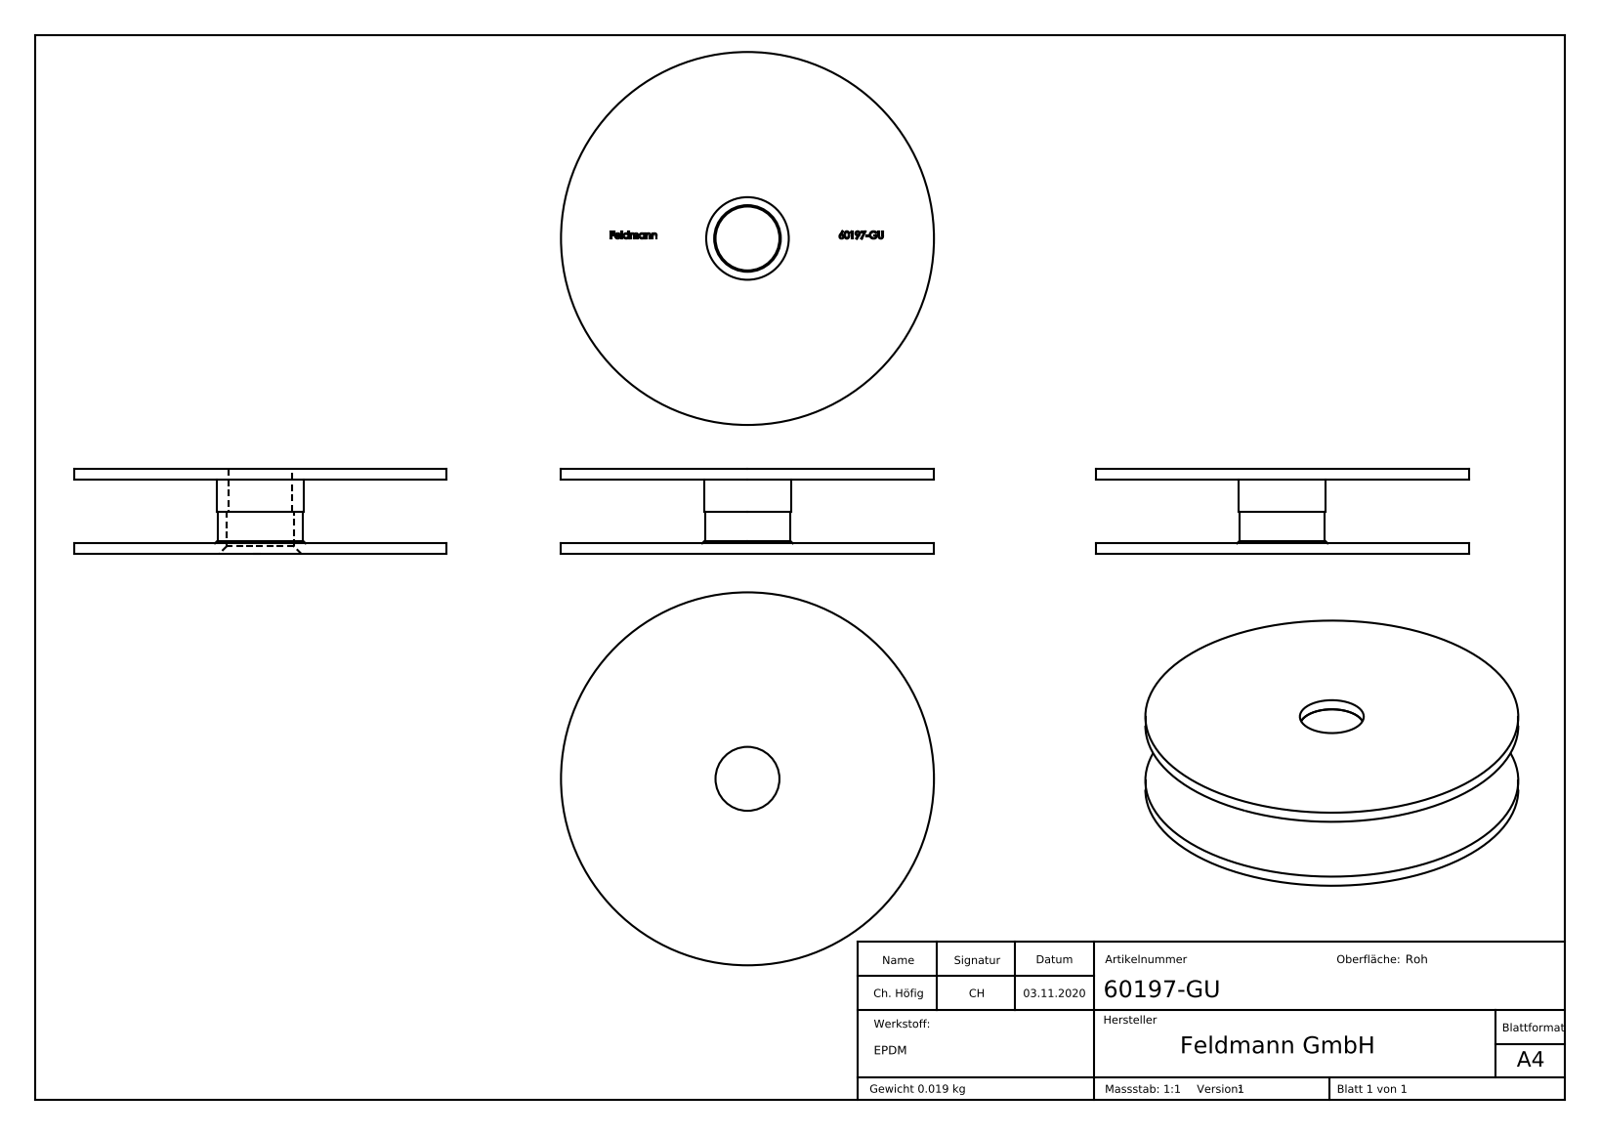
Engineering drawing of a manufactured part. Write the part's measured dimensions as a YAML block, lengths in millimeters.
part_name: "60197-GU Teil2_60197-GU Teil2; 60197-GU Teil1; 60197-GU; 60197-GU Teil1_60197-GU Teil1 (+3 more)"
step_written_by: "SolidWorks 2018 (CONFIG_CONTROL_DESIGN)"
units: millimeters
bodies: {solids: 3, faces: 224, planar: 115, cylindrical: 14, other: 95}
overall_size: [70, 70, 16]
volume: 15924
surface_area: 17180
round_holes:
  - {diameter: 12, count: 1}
  - {diameter: 12.5, count: 1}
round_bosses_or_shafts:
  - {diameter: 70, count: 1}
  - {diameter: 16.3, count: 1}
  - {diameter: 16, count: 1}
face_to_face_distances: [2, 14, 16, 12, 8, 6, 1.9, 7.9, 13.9, 15.9]
